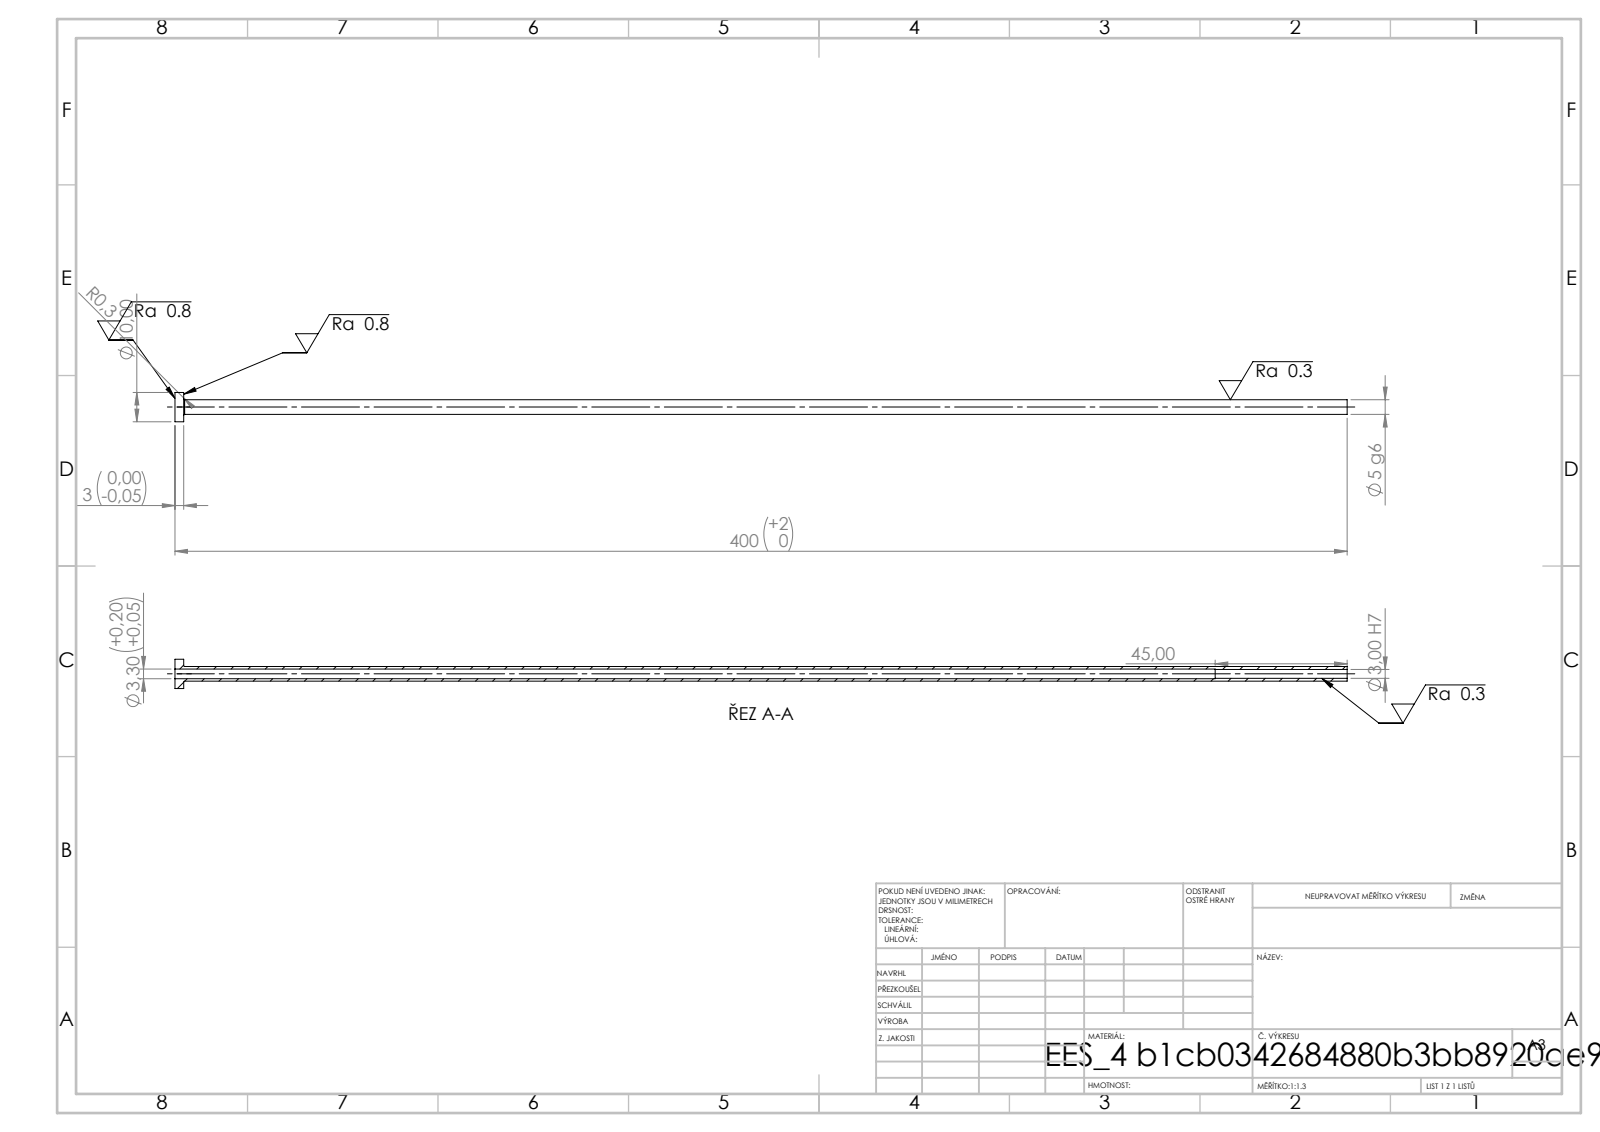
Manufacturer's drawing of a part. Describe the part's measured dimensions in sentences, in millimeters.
Its 3-D file was written by "SolidWorks 2019 (CONFIG_CONTROL_DESIGN)". It is 1 solid with 14 faces: 4 planar, 8 cylindrical and 2 other. Overall it measures 400 by 10 by 10 millimeters. Its volume is 4 677 cubic millimeters and its surface area 10 576 square millimeters. Round holes: 1 of diameter 3, 1 of diameter 3.3. Round bosses or shafts: 1 of diameter 10, 1 of diameter 5. The main face-to-face distances are 3, 400, 397, 355, 352, 45.
